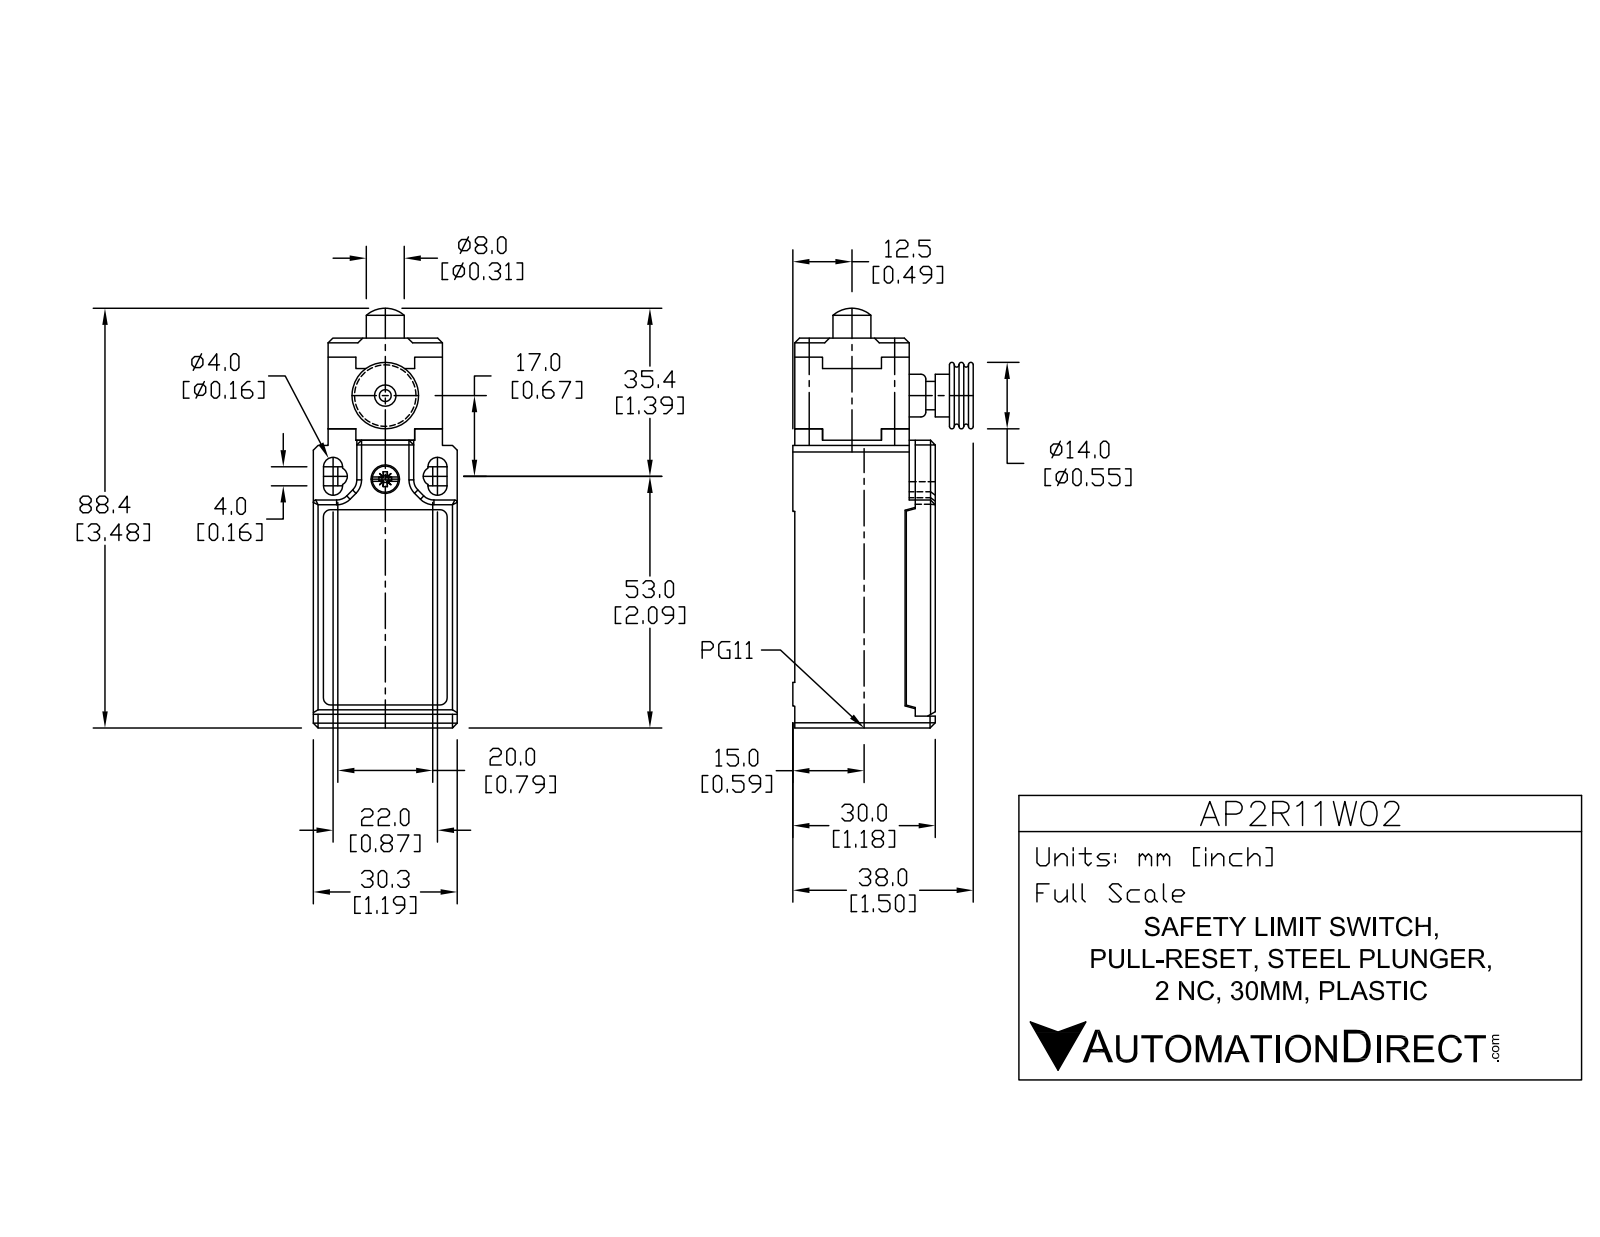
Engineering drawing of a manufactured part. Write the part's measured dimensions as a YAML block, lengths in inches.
part_name: "AP2R11W02"
step_written_by: "SolidWorks 2017 (AUTOMOTIVE_DESIGN)"
units: inches
bodies: {solids: 4, faces: 230, planar: 116, cylindrical: 78, other: 36}
overall_size: [3.52, 1.474, 1.193]
volume: 3.957
surface_area: 25.84
round_holes:
  - {diameter: 0.319, count: 1}
  - {diameter: 0.669, count: 1}
  - {diameter: 0.748, count: 1}
round_bosses_or_shafts:
  - {diameter: 0.22, count: 4}
  - {diameter: 0.217, count: 3}
  - {diameter: 0.386, count: 1}
  - {diameter: 0.354, count: 1}
  - {diameter: 0.315, count: 1}
  - {diameter: 0.236, count: 1}
  - {diameter: 0.098, count: 1}
partial_cylinders:
  - {radius: 0.039, count: 10}
  - {radius: 0.118, count: 8}
  - {radius: 0.079, count: 6}
  - {radius: 0.02, count: 4}
  - {radius: 0.394, count: 1}
  - {radius: 0.4, count: 1}
face_to_face_distances: [1.193, 1.165, 0.945, 0.124, 1.069, 0.236, 0.594, 0.22, 0.094, 1.181]
hole_center_spacings: [0.083]
